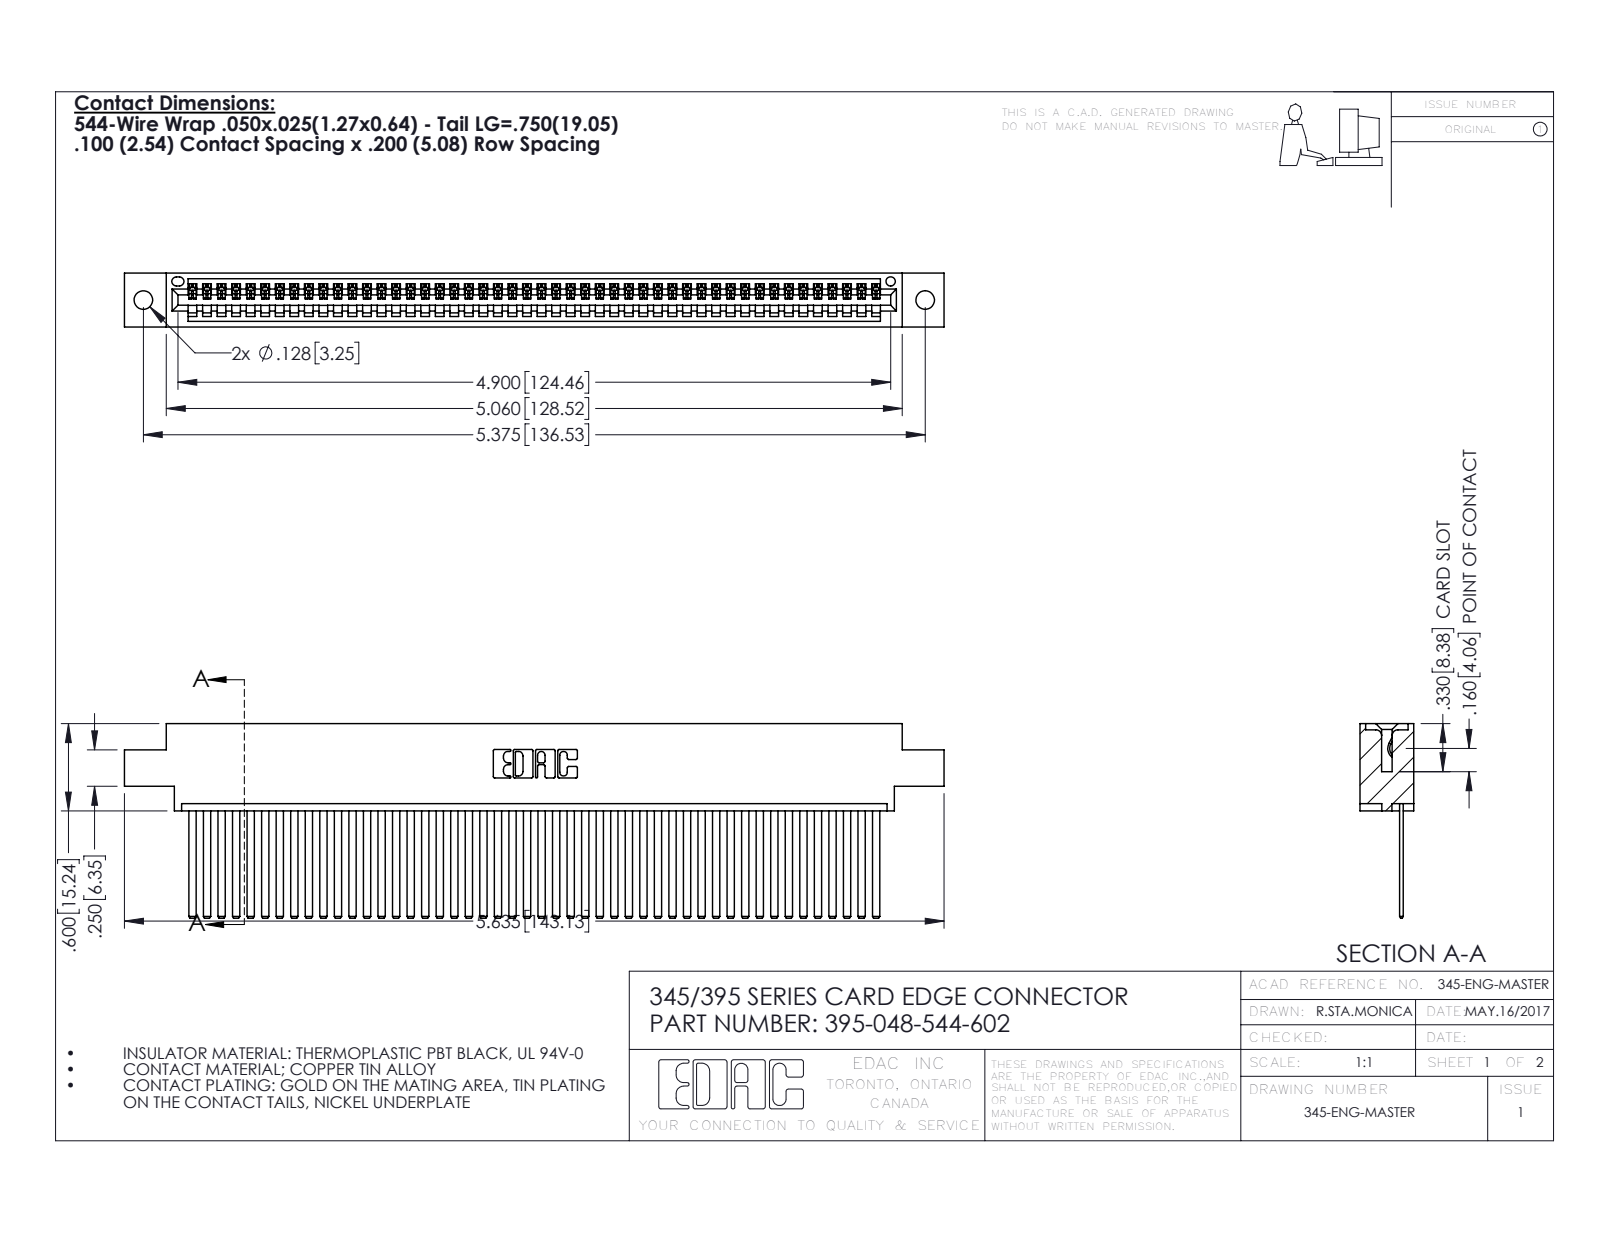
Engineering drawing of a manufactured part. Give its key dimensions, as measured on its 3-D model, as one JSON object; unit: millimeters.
{"part_name": "345-292-001_345-293-144; 395-048-544-602; 345 Part_0.170 Offset - 0.128 Dia", "step_written_by": "SolidWorks 2016 (CONFIG_CONTROL_DESIGN)", "units": "millimeters", "bodies": {"solids": 49, "faces": 2626, "planar": 1812, "cylindrical": 814, "other": 0}, "overall_size": [143.1, 34, 9.4], "volume_mm3": 14000, "surface_area_mm2": 20280, "round_holes": [[3.3, 2], [1.6, 1]], "partial_cylinders_radius": [[0.2, 96], [0.3, 22], [0.2, 6], [0.8, 6], [0.7, 3], [0.8, 2], [1, 2], [0.4, 1]], "face_to_face_distances": [1.8, 7.6, 0.6, 2.5, 6.9, 9.4, 5.1, 5.7, 4.4, 3.8], "hole_center_spacings": [6.9, 130.5, 136.5]}
